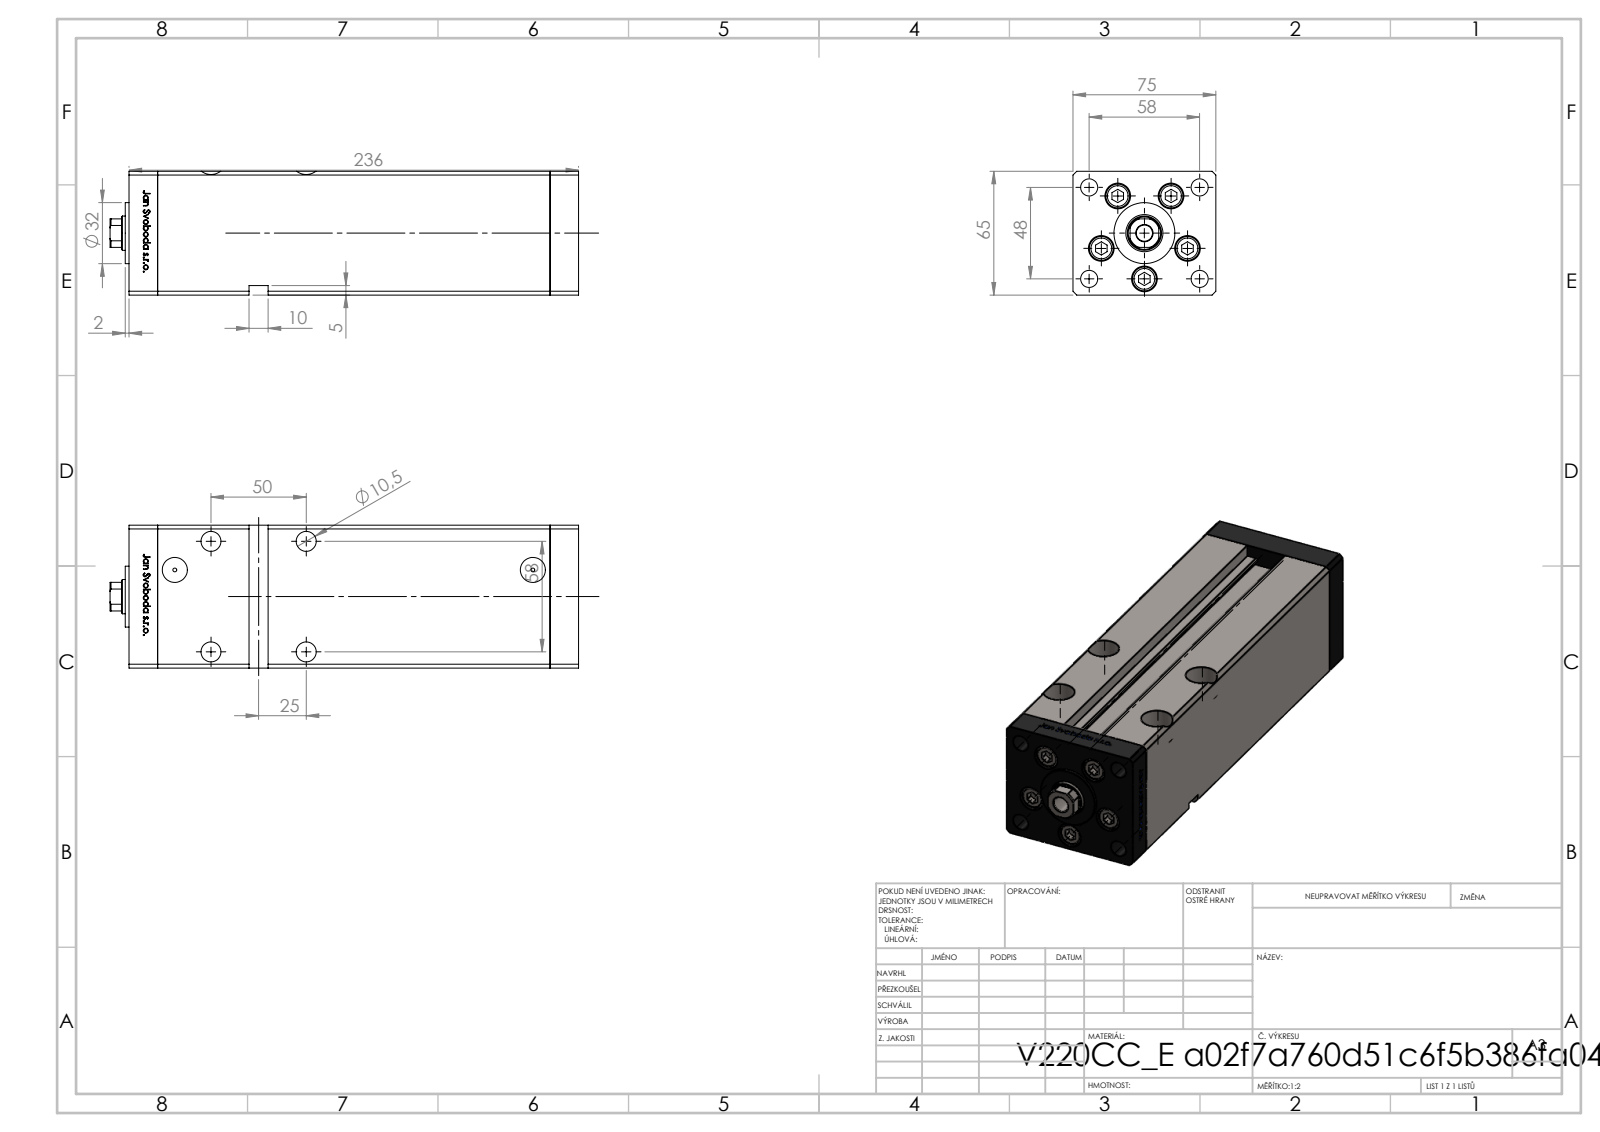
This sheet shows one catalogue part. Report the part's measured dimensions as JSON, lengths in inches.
{"part_name": "V220C_VC_E; V220C_E MIDDLE; ALLEN BOLT; V220C BACK_E (+1 more)", "step_written_by": "SolidWorks 2019 (CONFIG_CONTROL_DESIGN)", "units": "inches", "bodies": {"solids": 14, "faces": 1212, "planar": 473, "cylindrical": 165, "other": 574}, "overall_size": [9.685, 2.953, 2.559], "volume_in3": 59.55, "surface_area_in2": 262.7, "round_holes": [[0.354, 9], [0.531, 5], [0.413, 4], [0.65, 4], [0.079, 2], [0.518, 2], [0.335, 1], [0.709, 1], [0.768, 1]], "round_bosses_or_shafts": [[0.492, 5], [0.315, 5], [1.26, 1]], "partial_cylinders_radius": [[0.037, 2], [0.335, 1]], "face_to_face_distances": [2.953, 2.559, 0.591, 8.11, 8.701, 9.291, 2.146, 0.413, 1.033, 1.919], "hole_center_spacings": [0.945, 1.482, 2.283, 0.617, 0.678, 1.091, 1.135, 1.142]}
